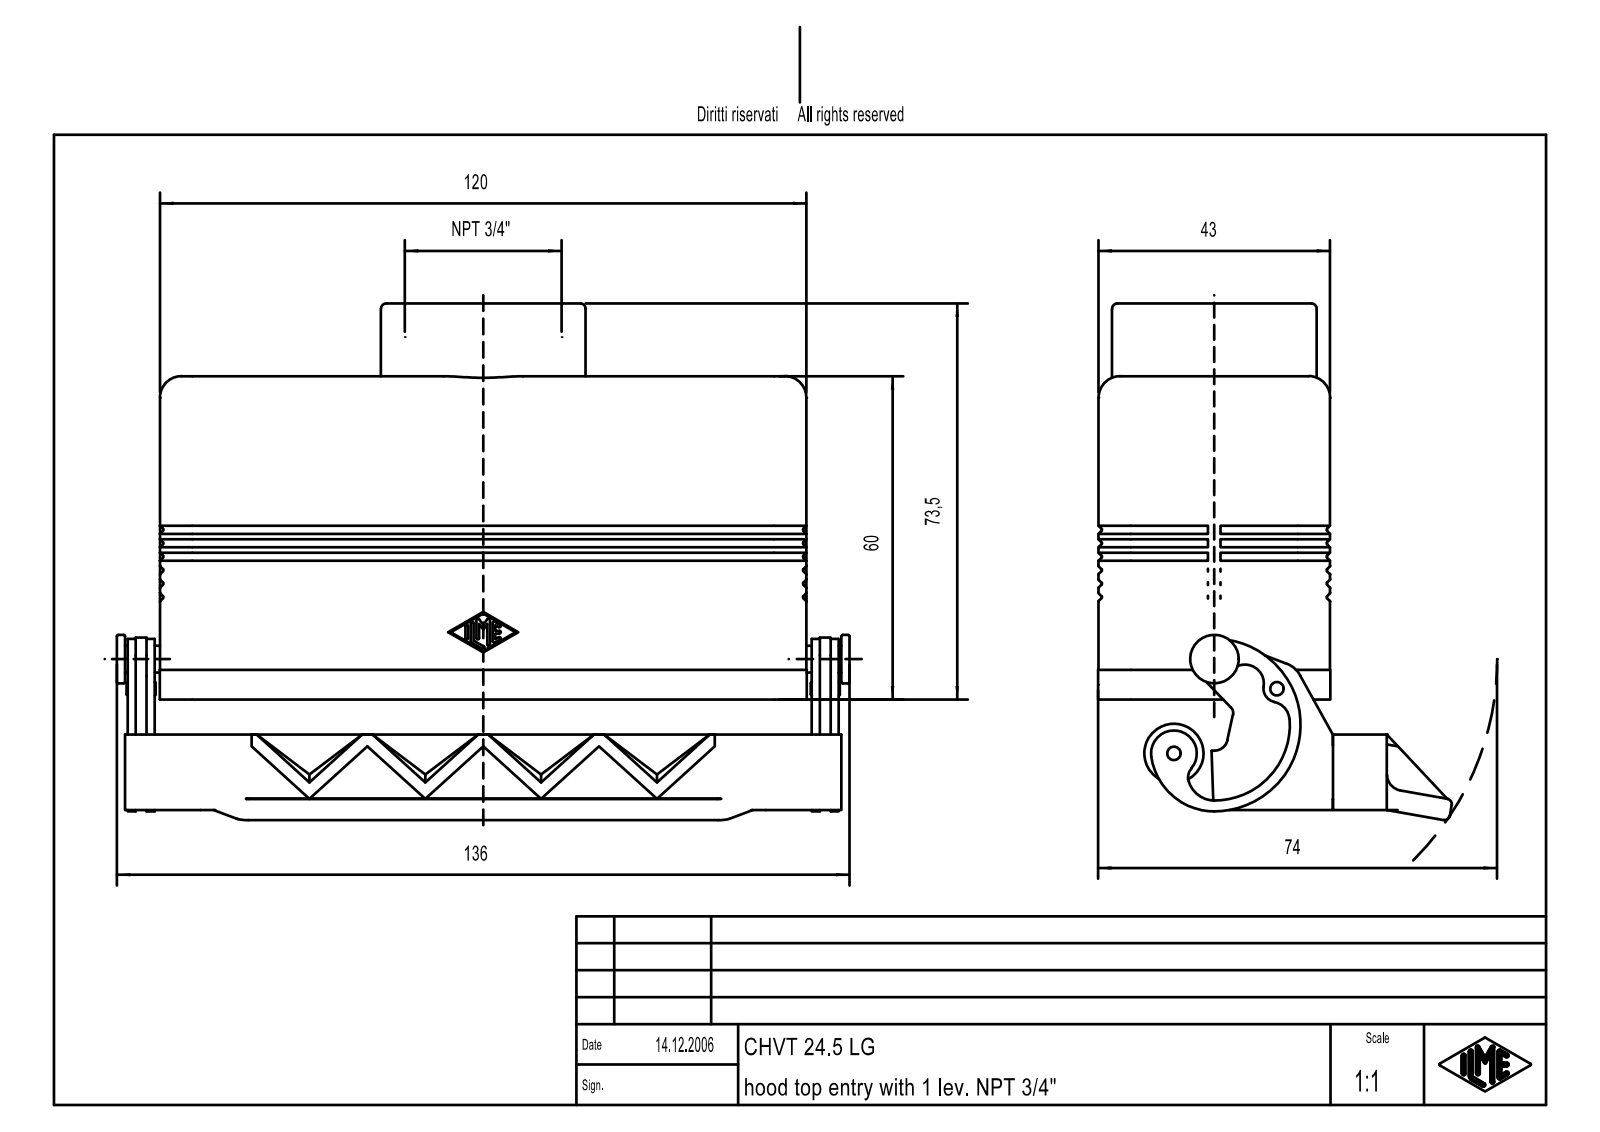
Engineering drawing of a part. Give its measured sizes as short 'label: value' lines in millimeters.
name: MSBO15075
written by: Creo Elements/Direct Modeling 18.0B 02-Dec-2011 (C) Parametric Technology GmbH (AUTOMOTIVE_DESIGN)
unit: mm
bodies: 1 solid, 773 faces (333 planar, 245 cylindrical, 195 other)
size: 136 × 95.87 × 65.64
volume: 118 988 mm³; area: 62 119 mm²
holes: 4× ⌀2.01, 4× ⌀3.1, 1× ⌀2.5
bosses: 1× ⌀38, 1× ⌀11, 1× ⌀9, 1× ⌀5, 1× ⌀3.1, 1× ⌀2
rounds: 38× R0.25, 28× R0.2, 9× R2.5, 6× R1, 5× R1.5, 5× R4, 4× R2.45, 4× R6
face distances: 3.5, 39.5, 36, 43, 3.55, 116.5, 8, 4, 4.5, 10.05
hole spacings: 27, 104, 107.45
